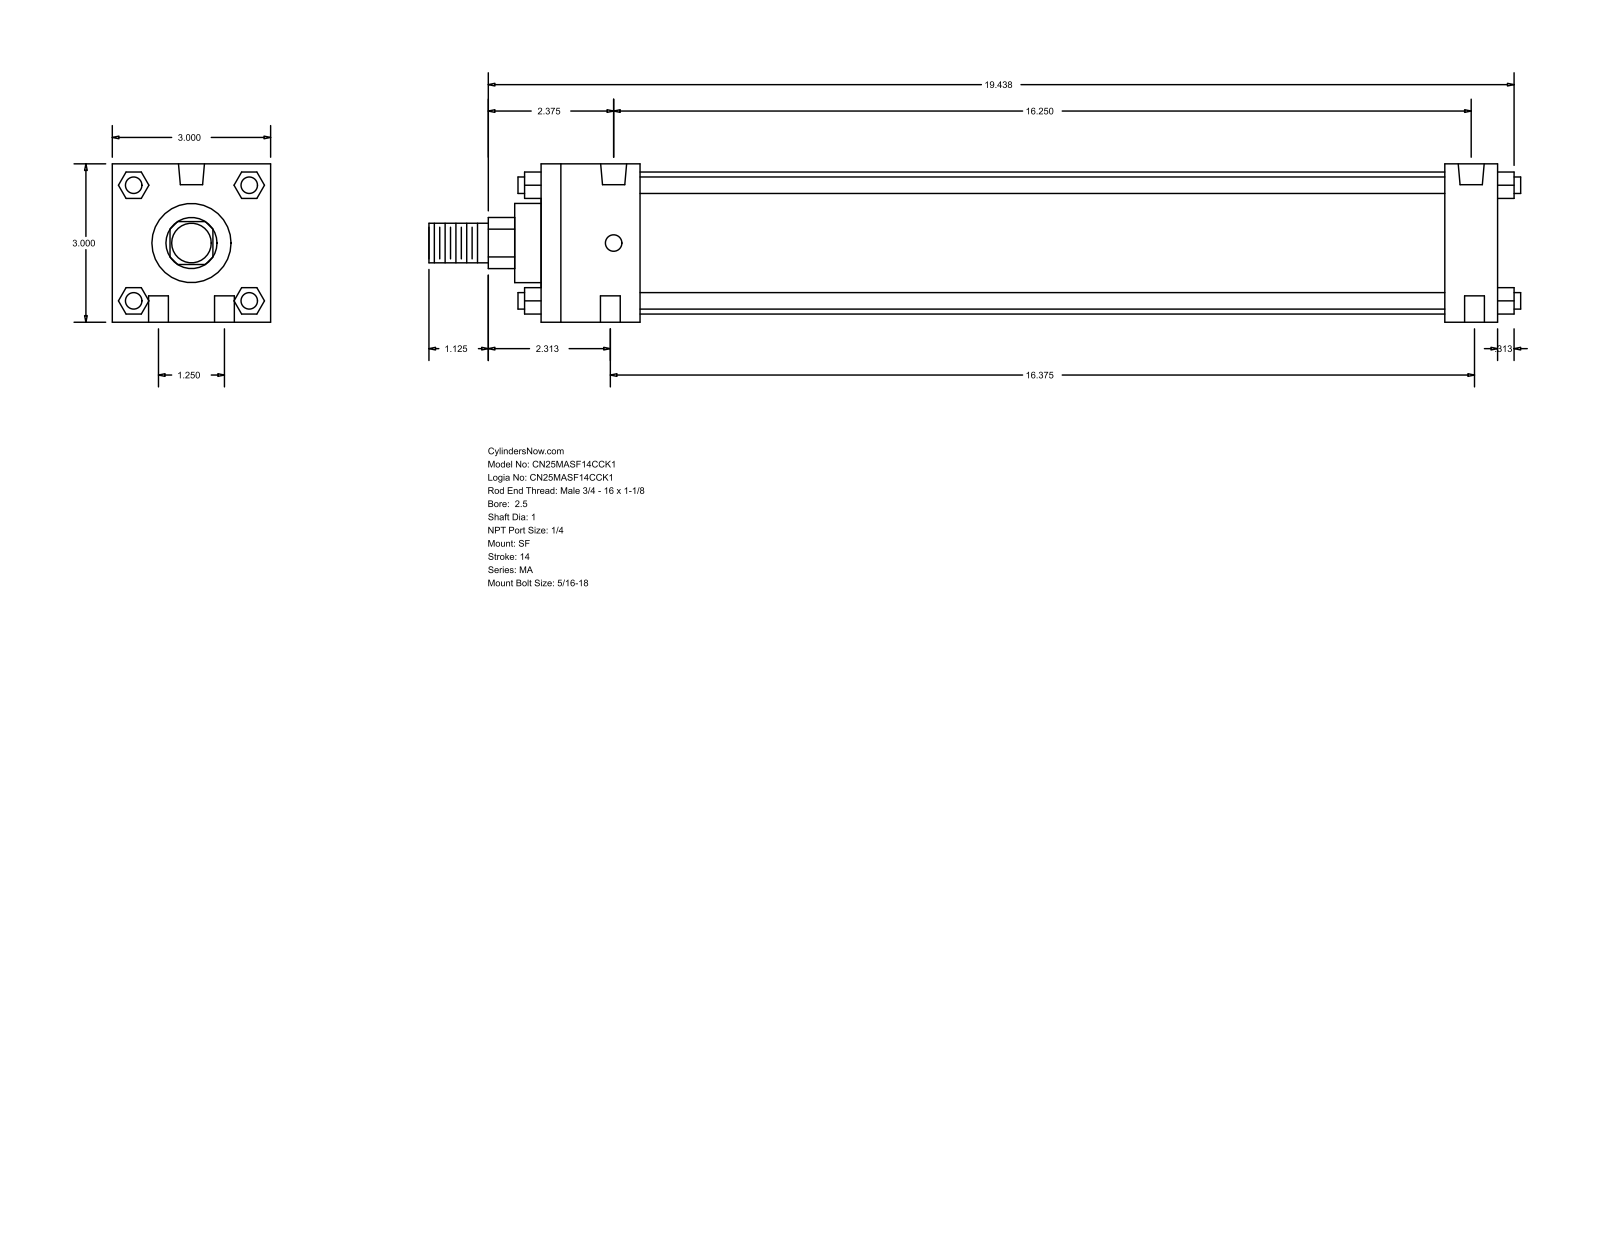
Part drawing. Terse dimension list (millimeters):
name: MA_SF__0250_1
written by: GSSL Pune (CONFIG_CONTROL_DESIGN)
unit: mm
bodies: 0 solids, 124 faces (94 planar, 30 cylindrical, 0 other)
size: 525.46 × 76.2 × 76.2
holes: 4× ⌀9.53, 2× ⌀7.94, 2× ⌀12.49
bosses: 4× ⌀7.94, 1× ⌀68.33, 1× ⌀38.1, 1× ⌀25.4, 1× ⌀19.05
rounds: 1× R12.29
face distances: 76.2, 460.37, 12.7, 434.98, 25.39, 47.63, 387.35, 412.74, 27.81, 48.17
hole spacings: 15.96, 414.63, 31.76, 412.74, 415.92, 417.13
